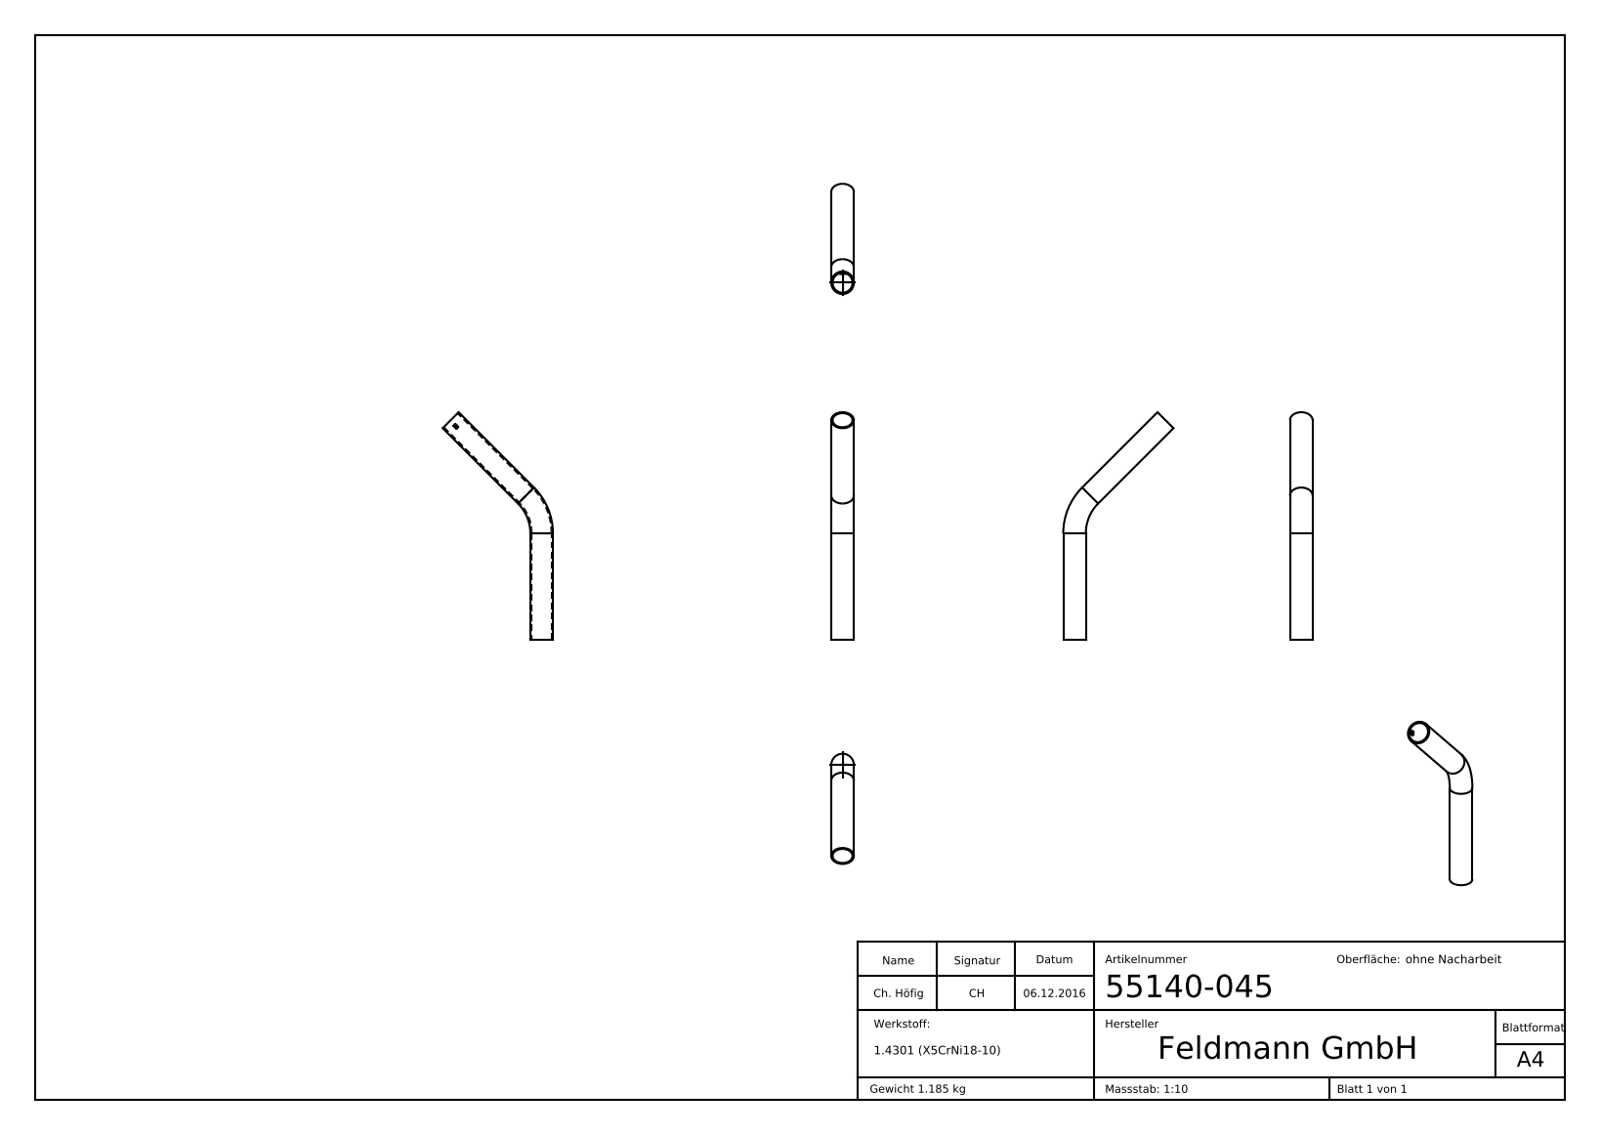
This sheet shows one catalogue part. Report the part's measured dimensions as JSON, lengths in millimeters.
{"part_name": "55140-045", "step_written_by": "SolidWorks 2015 (CONFIG_CONTROL_DESIGN)", "units": "millimeters", "bodies": {"solids": 1, "faces": 236, "planar": 110, "cylindrical": 32, "other": 94}, "overall_size": [427.12, 206.9, 42.4], "volume_mm3": 149961, "surface_area_mm2": 120606, "round_holes": [[37.4, 2]], "round_bosses_or_shafts": [[42.4, 2]], "partial_cylinders_radius": [[18.8, 1]], "face_to_face_distances": [1.23, 0.88, 3.66, 0.38, 3.38, 0.39, 3.64, 2.99, 2.97, 2.41]}
